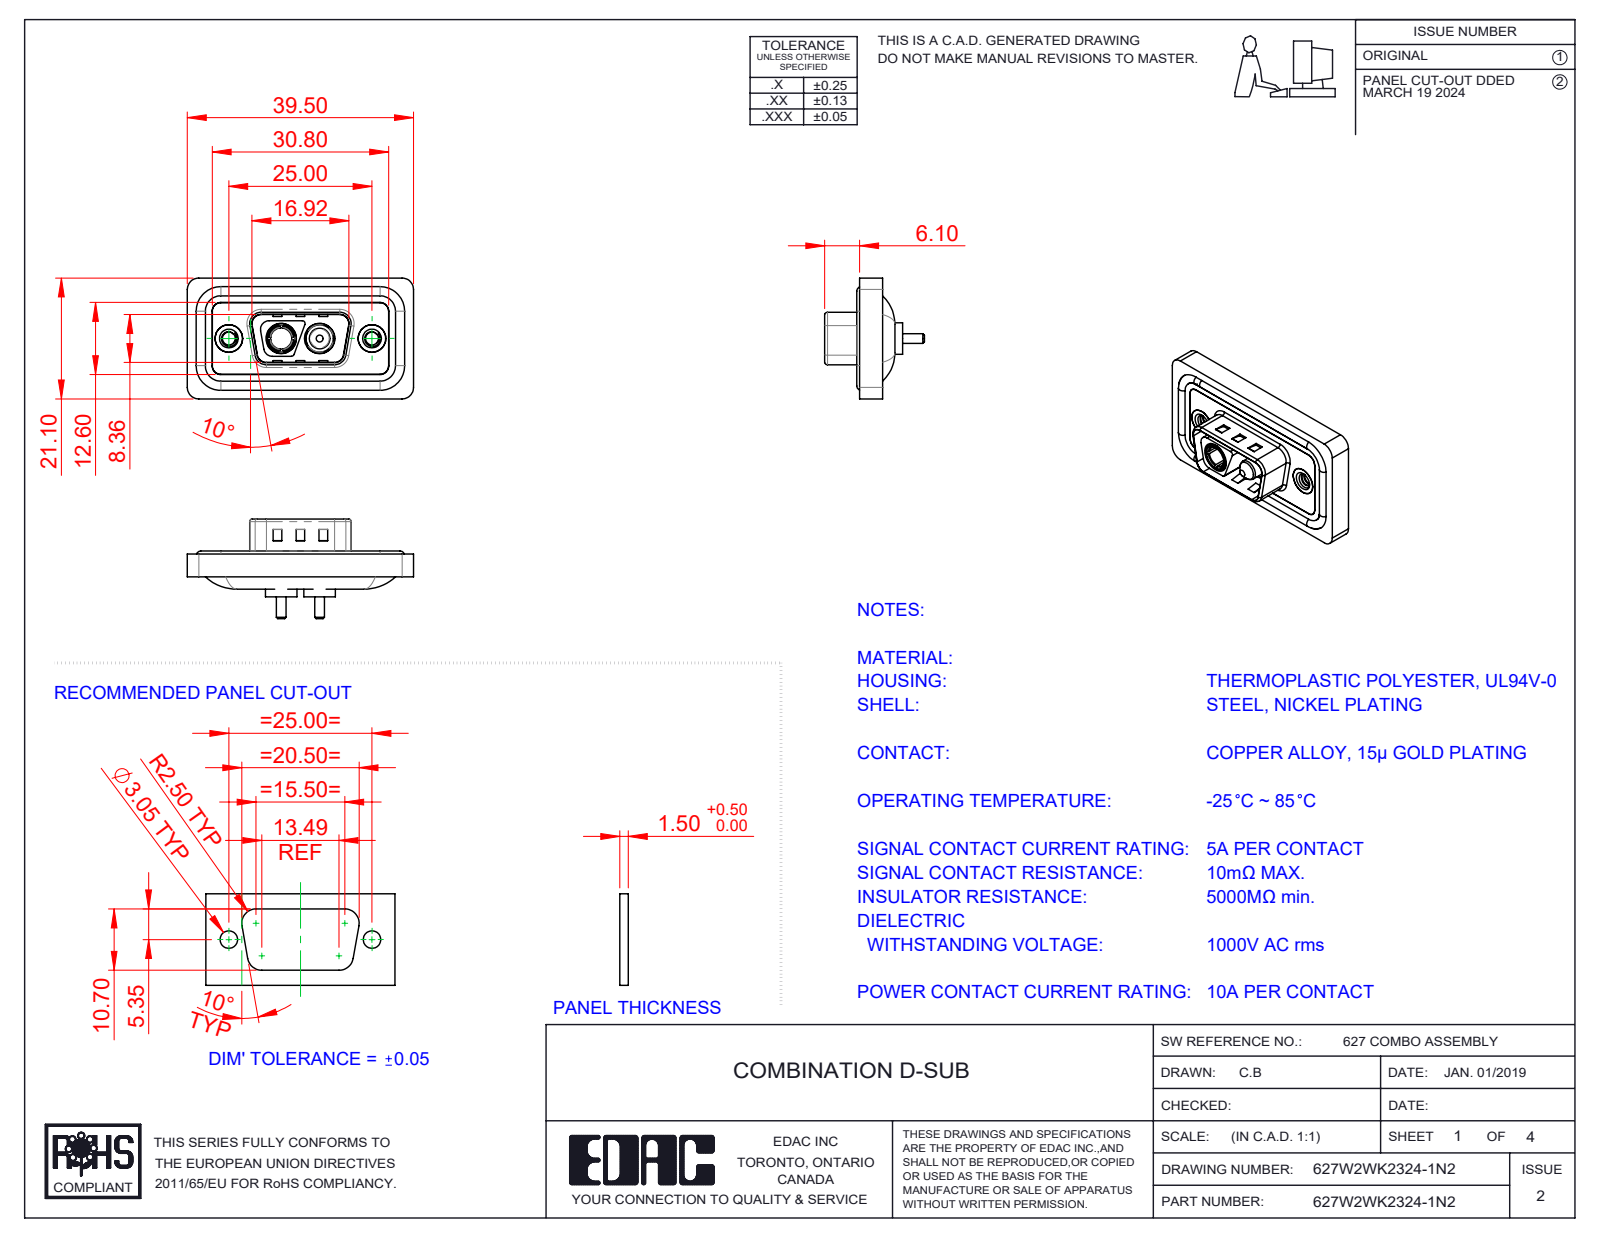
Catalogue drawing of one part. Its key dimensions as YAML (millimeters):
part_name: "627Combo Threaded Rivet_2; Power Socket_10A S; 627Combo Waterproof Housing_09 Contacts; 627Combo Shell Front_09 Contacts (+4 more)"
step_written_by: "SolidWorks 2023 (CONFIG_CONTROL_DESIGN)"
units: millimeters
bodies: {solids: 11, faces: 534, planar: 189, cylindrical: 227, other: 118}
overall_size: [39.5, 21.1, 17.4]
volume: 4525
surface_area: 7317
round_holes:
  - {diameter: 2.26, count: 2}
  - {diameter: 4, count: 2}
  - {diameter: 4.8, count: 2}
  - {diameter: 4.85, count: 2}
  - {diameter: 5, count: 2}
  - {diameter: 5.3, count: 2}
  - {diameter: 3.7, count: 1}
round_bosses_or_shafts:
  - {diameter: 1.6, count: 4}
  - {diameter: 5.5, count: 2}
  - {diameter: 5.2, count: 2}
  - {diameter: 4.9, count: 2}
  - {diameter: 4.75, count: 2}
  - {diameter: 3.75, count: 2}
  - {diameter: 1.7, count: 2}
  - {diameter: 4.96, count: 1}
partial_cylinders:
  - {radius: 1.5, count: 24}
  - {radius: 2, count: 18}
  - {radius: 0.5, count: 10}
  - {radius: 1.6, count: 8}
  - {radius: 0.25, count: 4}
  - {radius: 0.6, count: 4}
  - {radius: 0.65, count: 4}
  - {radius: 0.9, count: 4}
face_to_face_distances: [0.4, 1.1, 2.9, 0.5, 3.1, 1.6, 1.5, 4, 2.5, 1.8]
hole_center_spacings: [9.14, 15.86, 6.72, 25]
